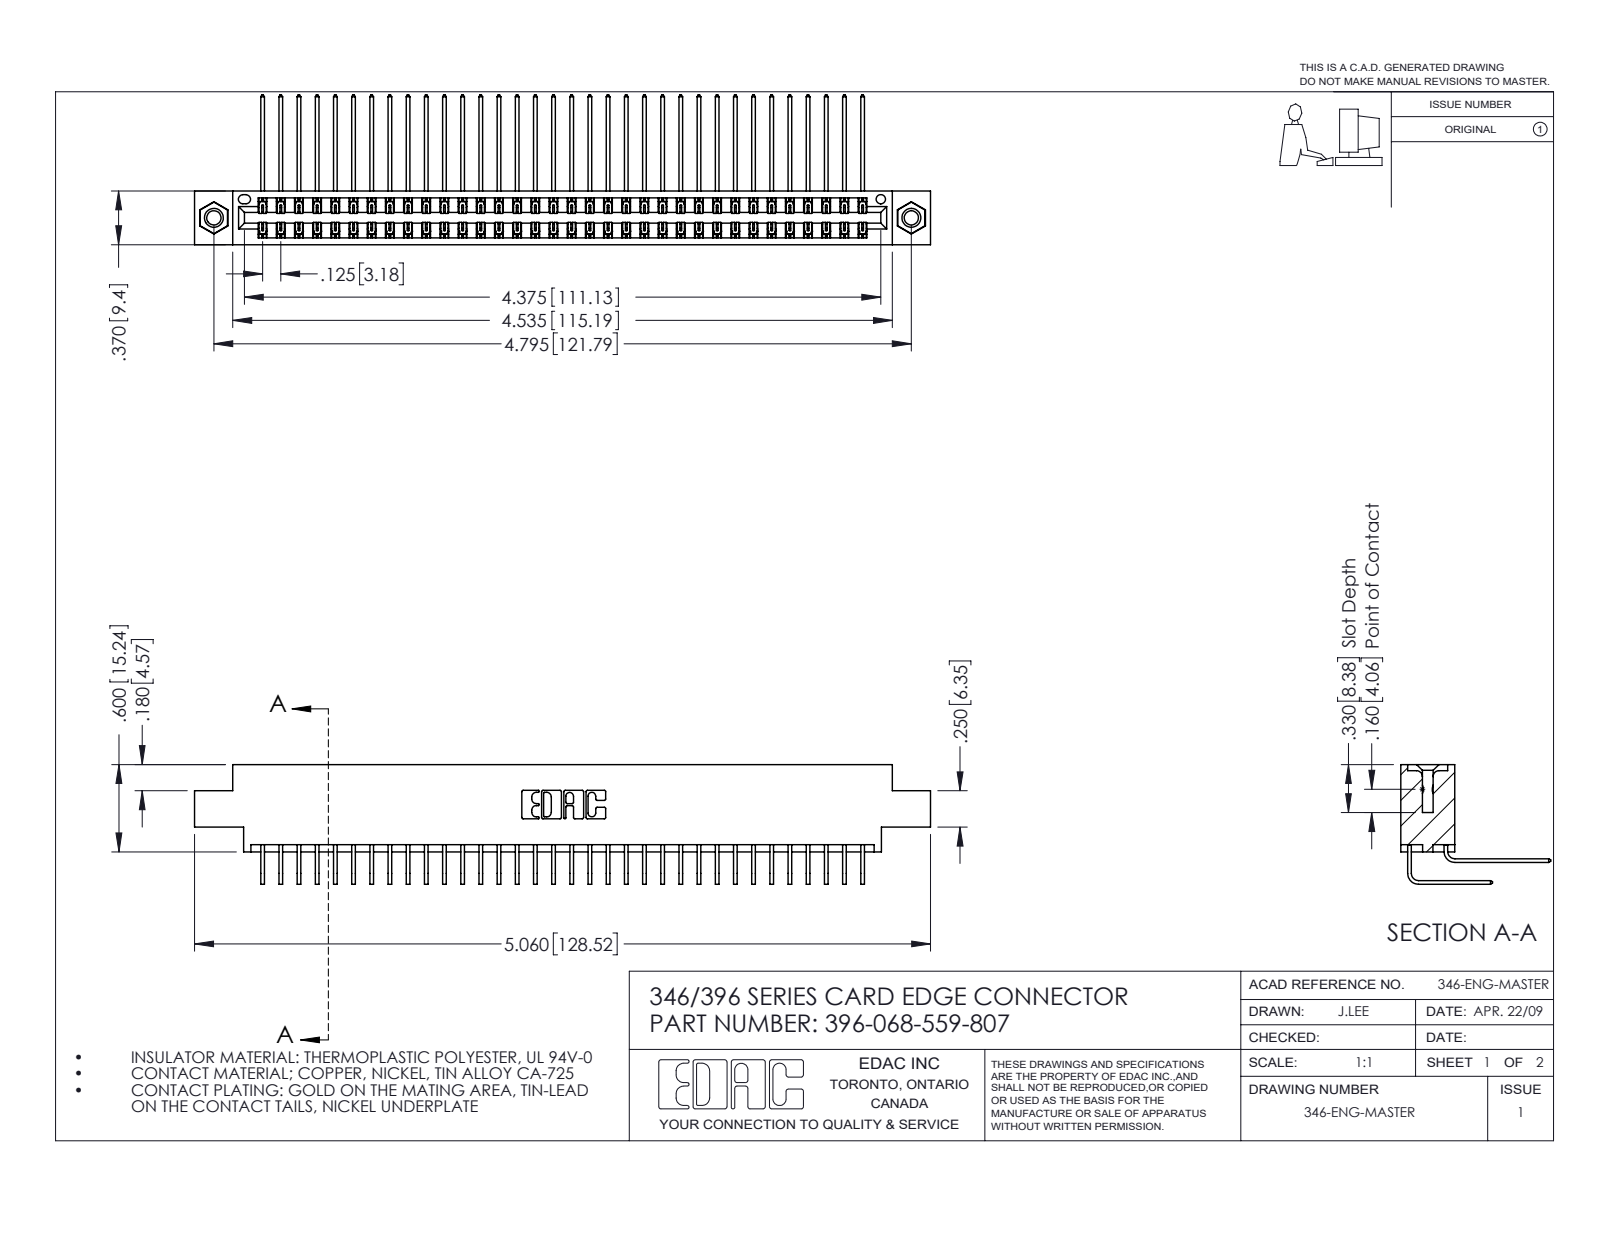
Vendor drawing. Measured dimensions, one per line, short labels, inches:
name: 345-250-001_345-250-005-103; 345-292-001_559 Tail - 2; 346 Part_0.170 Offset - 0.156 Dia-TI; 396-068-559-807 (+1 more)
written by: SolidWorks 2016 (CONFIG_CONTROL_DESIGN)
unit: in
bodies: 71 solids, 3858 faces (2628 planar, 1214 cylindrical, 16 other)
size: 5.06 × 1.03 × 0.823
volume: 0.775 in³; area: 30.1 in²
holes: 2× ⌀0.098, 2× ⌀0.125, 2× ⌀0.156, 1× ⌀0.064
bosses: 2× ⌀0.155
rounds: 102× R0.006, 22× R0.01, 6× R0.007, 6× R0.031, 3× R0.026, 2× R0.014, 2× R0.022, 2× R0.024
face distances: 0.048, 0.322, 0.025, 0.37, 0.25, 0.072, 0.298, 0.275, 0.222, 0.148
hole spacings: 0.246, 4.587, 4.795
